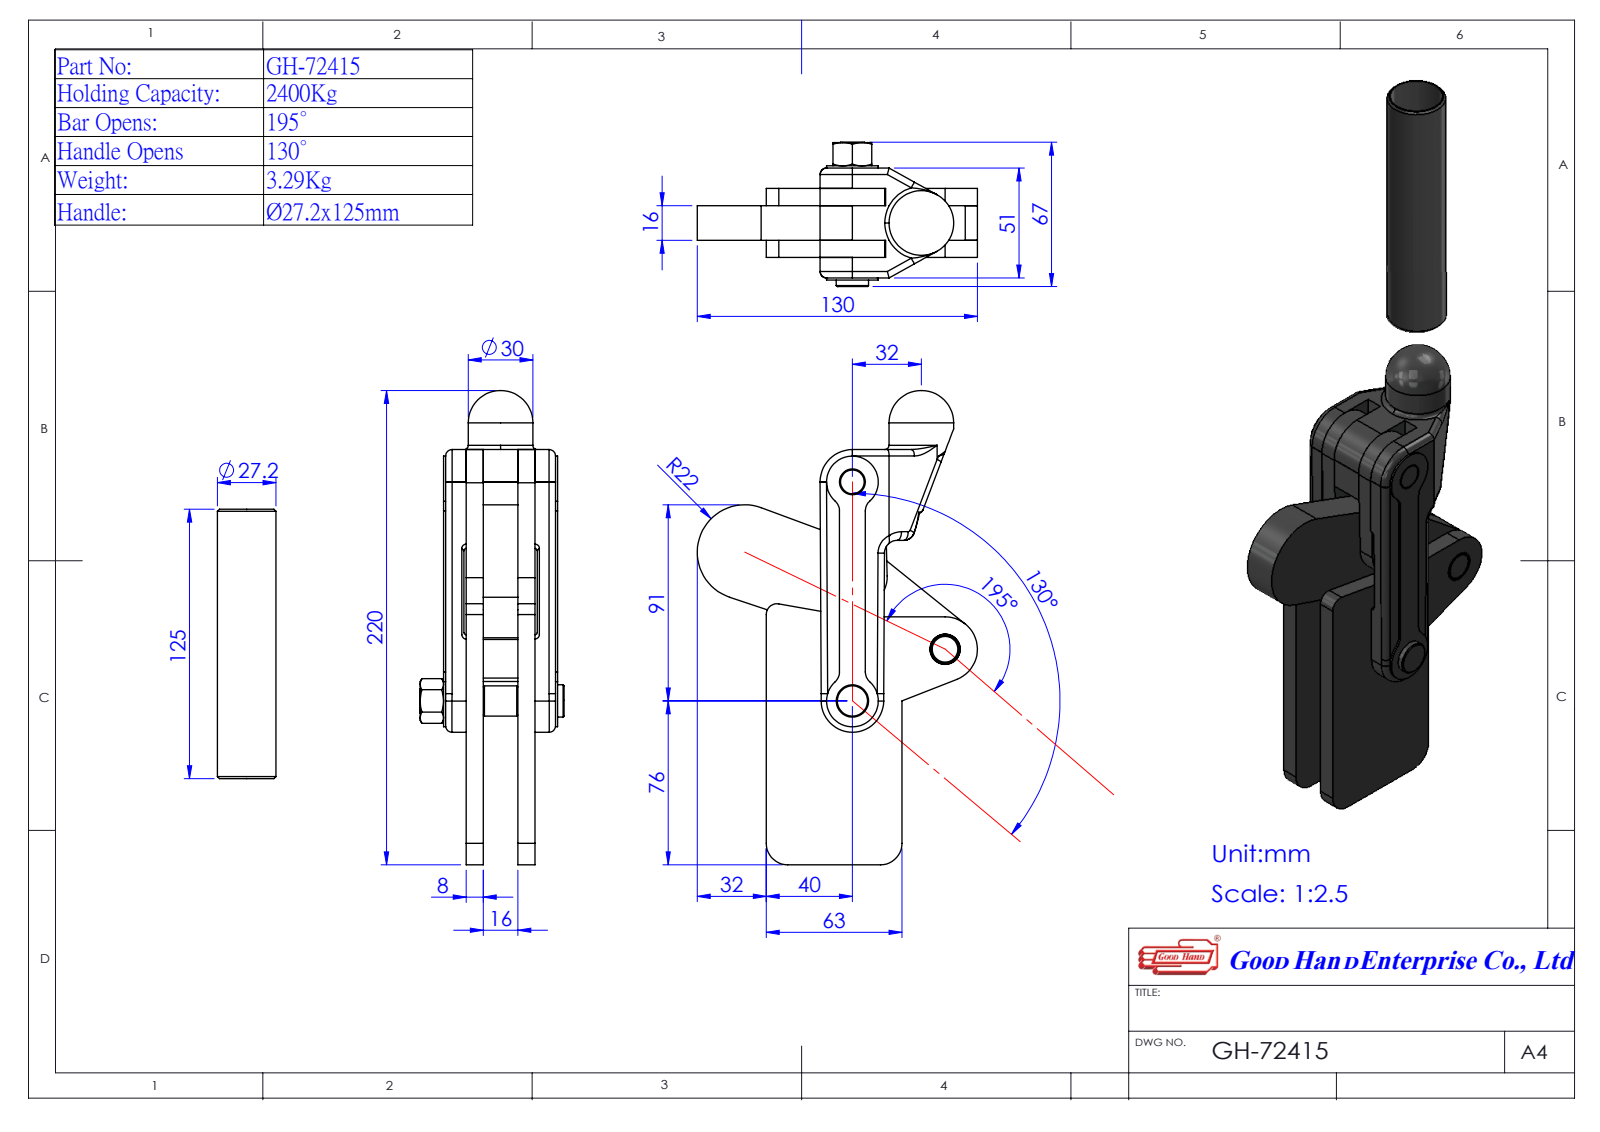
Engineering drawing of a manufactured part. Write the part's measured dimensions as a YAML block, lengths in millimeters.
part_name: "27241008-1^GH-72415(簡化)-1; 472410125-1^GH-72415(簡化)-1; Group2^GH-72415(簡化)-1; Group1^GH-72415(簡化)-1 (+2 more)"
step_written_by: "SolidWorks 2016 (AUTOMOTIVE_DESIGN)"
units: millimeters
bodies: {solids: 5, faces: 170, planar: 72, cylindrical: 78, other: 20}
overall_size: [346.85, 130, 66.8]
volume: 414157
surface_area: 120628
round_holes:
  - {diameter: 10, count: 4}
  - {diameter: 21.6, count: 1}
round_bosses_or_shafts:
  - {diameter: 30, count: 1}
  - {diameter: 27.2, count: 1}
  - {diameter: 15, count: 1}
partial_cylinders:
  - {radius: 6, count: 5}
  - {radius: 15, count: 4}
  - {radius: 3, count: 2}
  - {radius: 5, count: 2}
  - {radius: 10, count: 2}
  - {radius: 12, count: 2}
  - {radius: 14.5, count: 1}
  - {radius: 22, count: 1}
face_to_face_distances: [8, 24, 16, 32, 9.5, 17.5, 33.5, 41.5, 1, 10.5]
hole_center_spacings: [43.99, 49.24, 53.69, 57.63, 88.72, 101.6]
